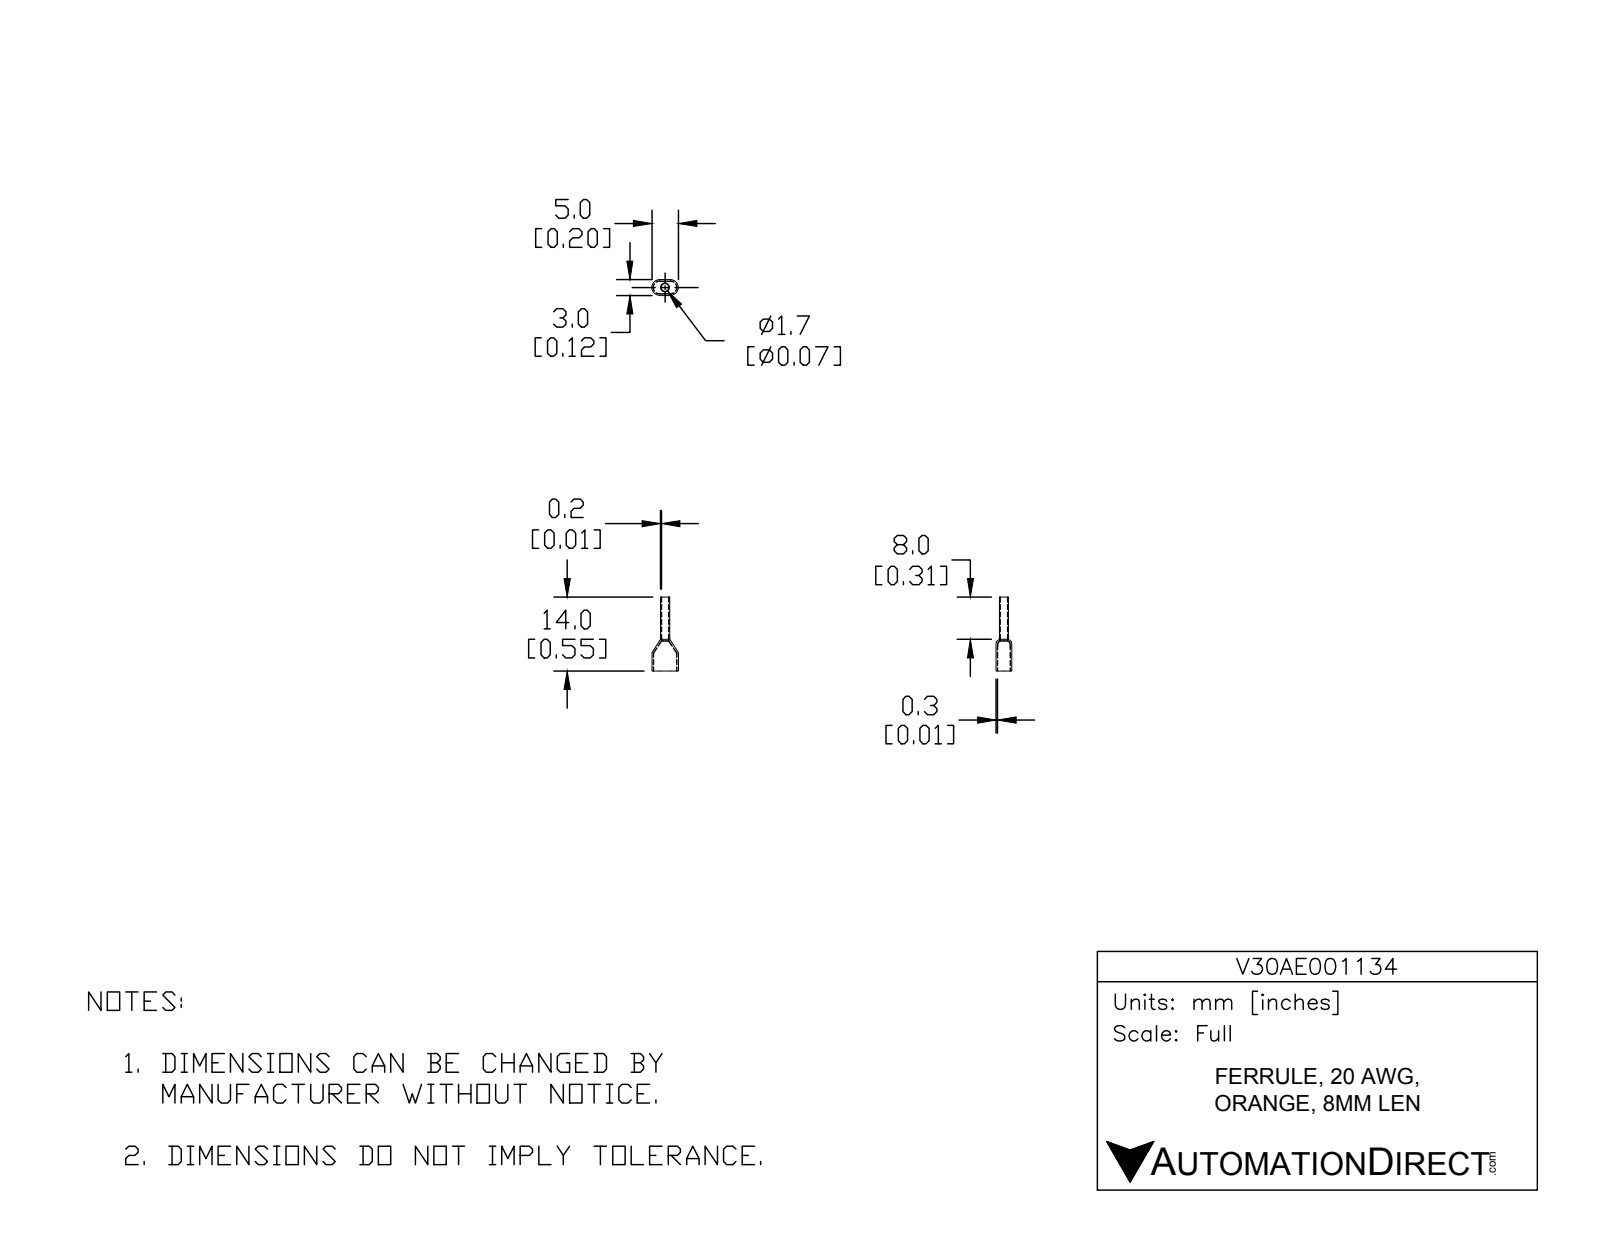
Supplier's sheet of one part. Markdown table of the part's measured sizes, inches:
| quantity | value |
| --- | --- |
| part name | V30AE001134 |
| STEP written by | SolidWorks 2017 (AUTOMOTIVE_DESIGN) |
| units | inches |
| bodies | 2 solids, 36 faces (14 planar, 22 cylindrical, 0 other) |
| overall size | 0.551 × 0.197 × 0.118 |
| volume | 0.002 in³ |
| surface area | 0.341 in² |
| round holes (diameter × count) | 0.055 × 1 |
| round bosses / shafts (diameter × count) | 0.067 × 1 |
| partial cylindrical surfaces (radius × count) | 0.047 × 6, 0.059 × 6 |
| main face-to-face distances | 0.106, 0.118, 0.094, 0.236, 0.551, 0.315, 0.224, 0.327 |
